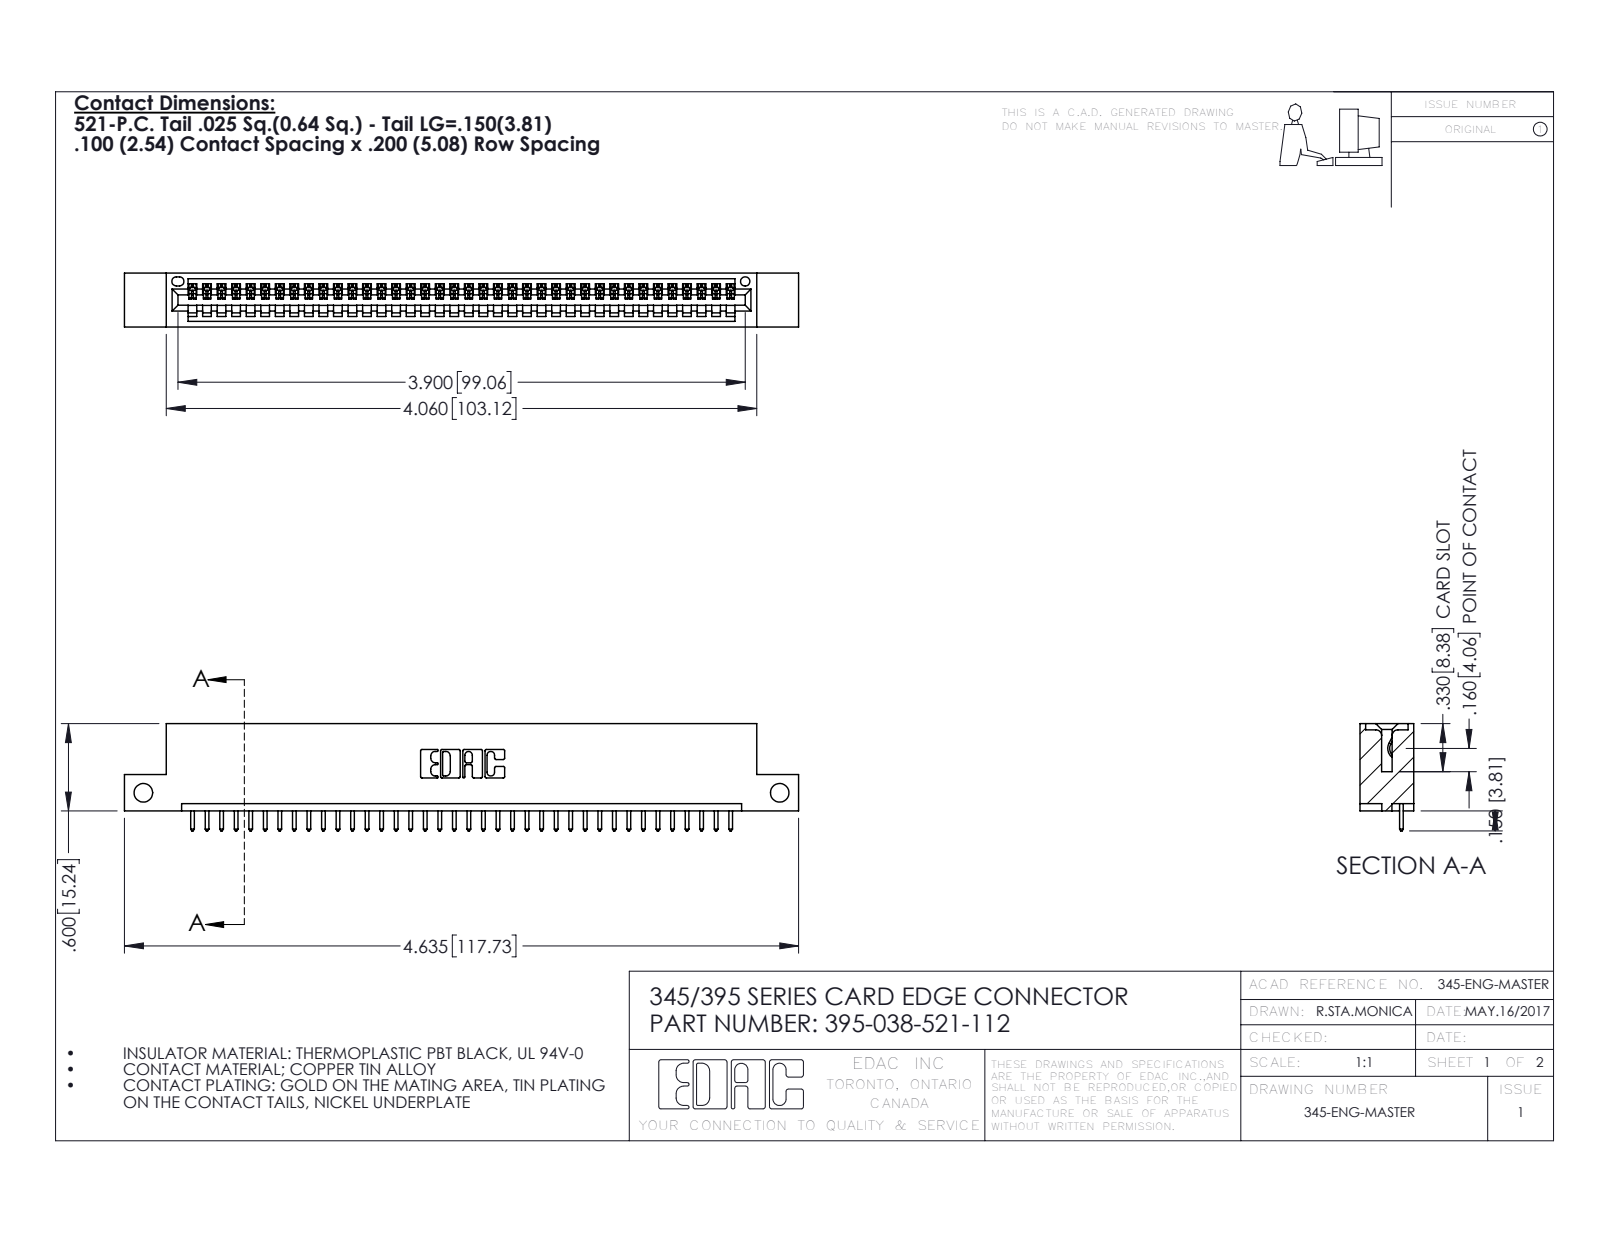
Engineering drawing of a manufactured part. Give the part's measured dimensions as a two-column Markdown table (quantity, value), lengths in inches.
| quantity | value |
| --- | --- |
| part name | 345-292-001_345-293-121; 395-038-521-112; 345 Part_Flush Mounting Lugs - Side Mount |
| STEP written by | SolidWorks 2016 (CONFIG_CONTROL_DESIGN) |
| units | inches |
| bodies | 39 solids, 2330 faces (1600 planar, 730 cylindrical, 0 other) |
| overall size | 4.635 × 0.737 × 0.37 |
| volume | 0.668 in³ |
| surface area | 21.6 in² |
| round holes (diameter × count) | 0.128 × 2, 0.064 × 1 |
| partial cylindrical surfaces (radius × count) | 0.006 × 76, 0.01 × 76, 0.01 × 22, 0.007 × 6, 0.031 × 6, 0.026 × 3, 0.031 × 2, 0.04 × 2 |
| main face-to-face distances | 0.298, 0.072, 0.2, 0.37, 0.098, 0.272, 0.025, 0.225, 0.149, 0.072 |
| hole center spacings | 4.375 |
